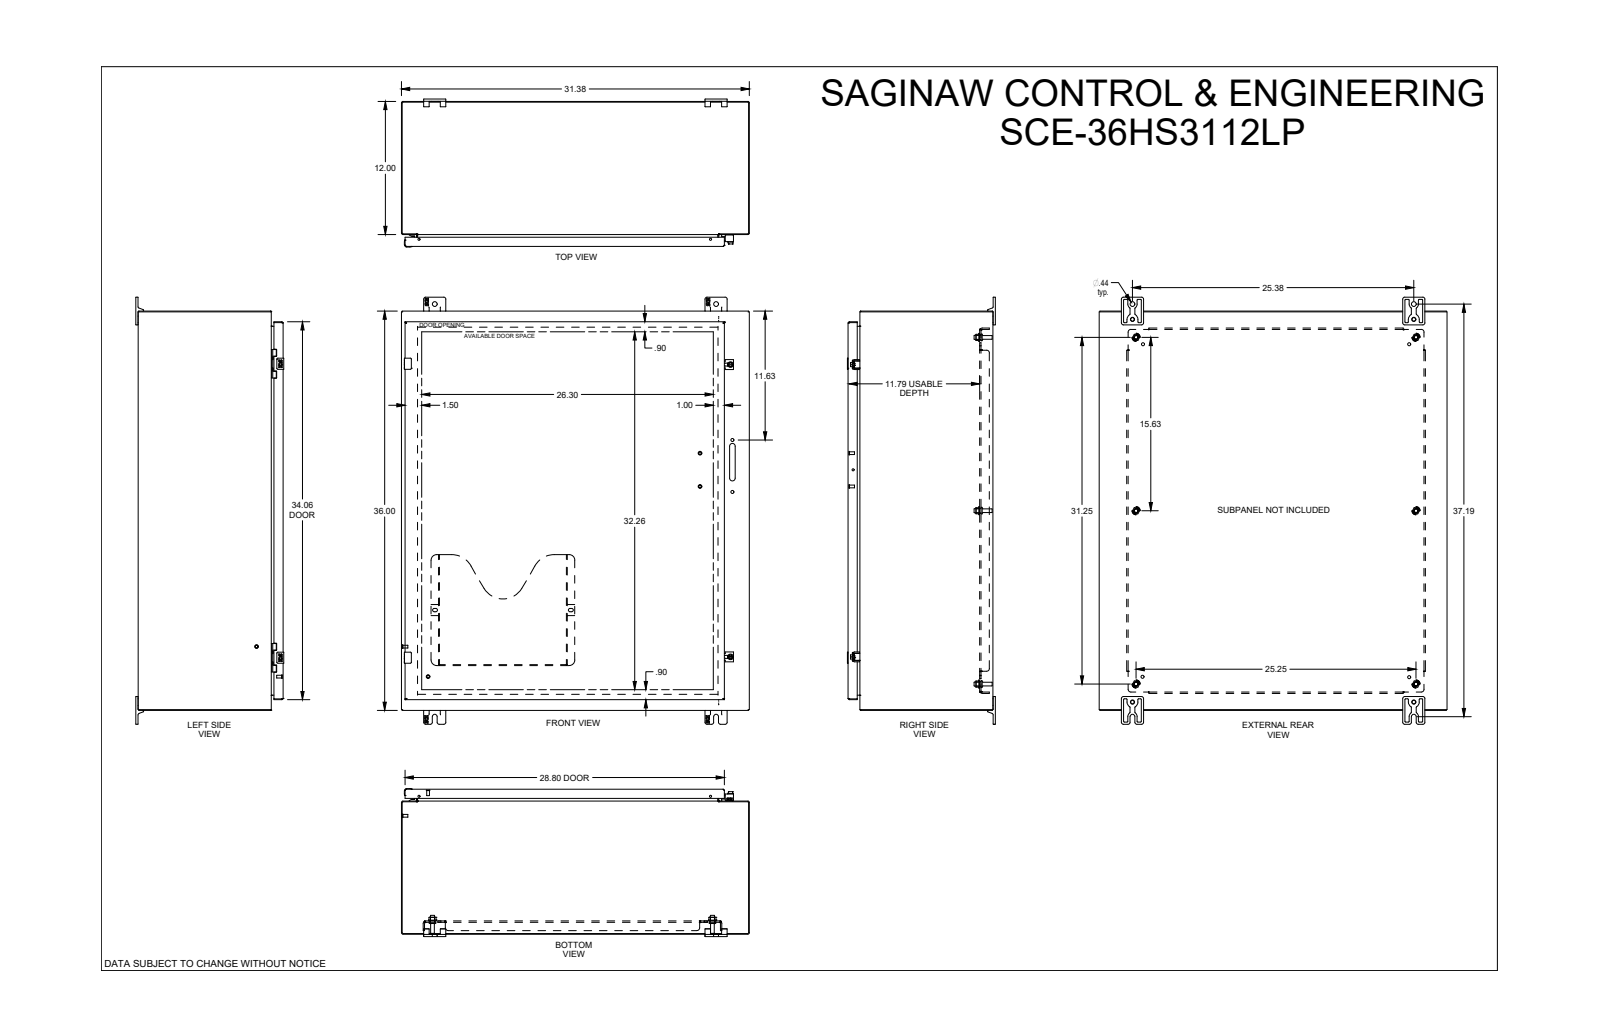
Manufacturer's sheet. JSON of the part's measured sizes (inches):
{"part_name": "SCE-36HS3112LP", "step_written_by": "SolidWorks 2021 (AUTOMOTIVE_DESIGN)", "units": "inches", "bodies": {"solids": 60, "faces": 3108, "planar": 1127, "cylindrical": 786, "other": 1195}, "overall_size": [38.5, 31.375, 13.343], "volume_in3": 468.6, "surface_area_in2": 10819, "round_holes": [[0.281, 6], [0.367, 6], [0.5, 6], [0.172, 4], [0.205, 4], [0.244, 4], [0.25, 4], [0.31, 4], [0.312, 4], [0.375, 4], [0.04, 2], [0.203, 2]], "round_bosses_or_shafts": [[0.248, 8], [0.366, 6], [0.332, 6], [0.25, 6], [0.17, 6], [0.59, 4], [0.563, 4], [0.376, 4]], "partial_cylinders_radius": [[0.01, 101], [0.025, 72], [0.029, 24], [0.185, 21], [0.015, 20], [0.04, 18], [0.043, 12], [0.118, 12]], "face_to_face_distances": [0.075, 12.993, 12.918, 13.068, 1.125, 1.2, 11.868, 11.793, 0.125, 1.075], "hole_center_spacings": [15.625, 29.694, 15.019, 25.25, 25.375, 28.843, 30.638, 39.306]}
